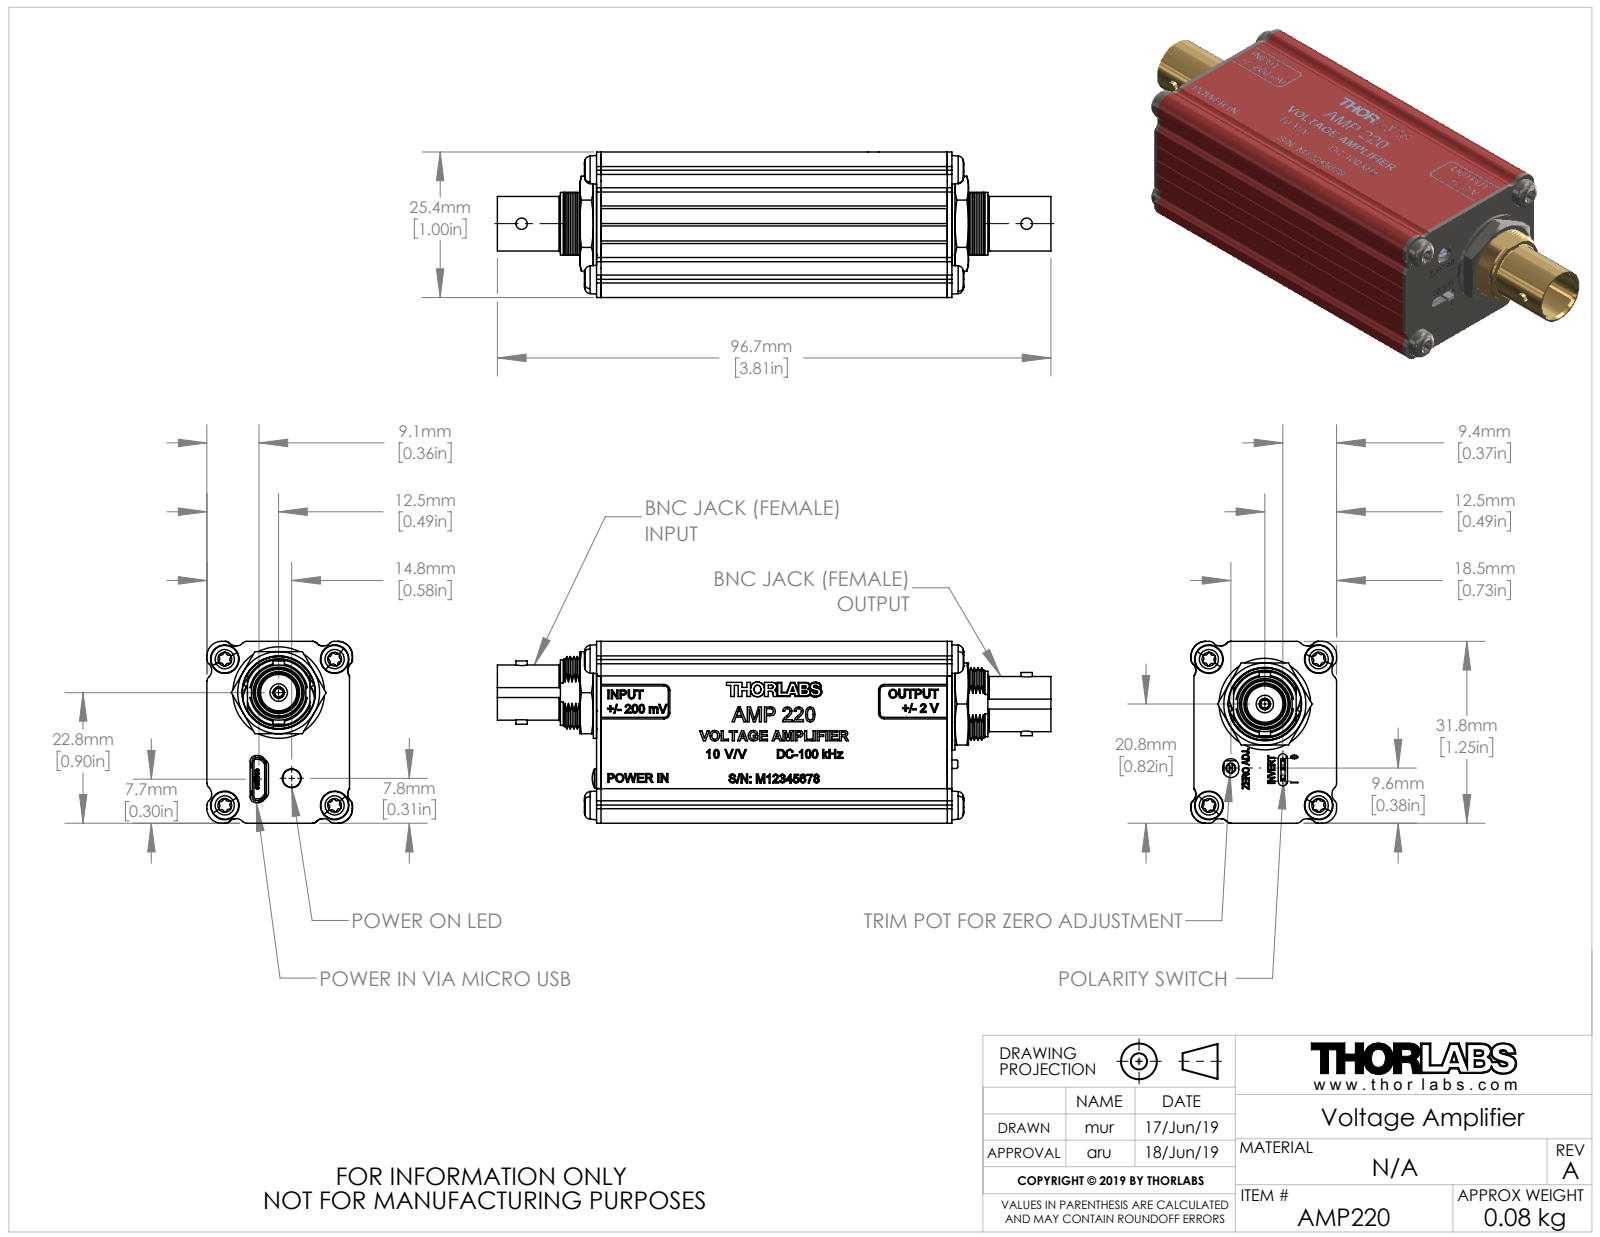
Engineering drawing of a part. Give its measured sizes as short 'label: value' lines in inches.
name: 19.08.22_AMP220 WEB
written by: SolidWorks 2018 (AUTOMOTIVE_DESIGN)
unit: in
bodies: 28 solids, 4301 faces (2662 planar, 694 cylindrical, 945 other)
size: 3.805 × 1.25 × 1
volume: 1.579 in³; area: 46.65 in²
holes: 4× ⌀0.008, 4× ⌀0.024, 4× ⌀0.138, 2× ⌀0.033, 2× ⌀0.035, 2× ⌀0.047, 2× ⌀0.059, 2× ⌀0.076, 2× ⌀0.159, 2× ⌀0.273, 2× ⌀0.349, 2× ⌀0.5
bosses: 6× ⌀0.018, 4× ⌀0.098, 4× ⌀0.087, 2× ⌀0.63, 2× ⌀0.45, 2× ⌀0.412, 2× ⌀0.38, 2× ⌀0.272
rounds: 48× R0.009, 48× R0.017, 26× R0.04, 25× R0.008, 20× R0.006, 14× R0.063, 12× R0.01, 11× R0.01
face distances: 0.05, 0.12, 0.065, 0.472, 0.031, 2.412, 0.36, 0.24, 0.48, 0.17
hole spacings: 0.044, 0.079, 0.157, 0.222, 0.277, 0.432, 0.496, 0.507
